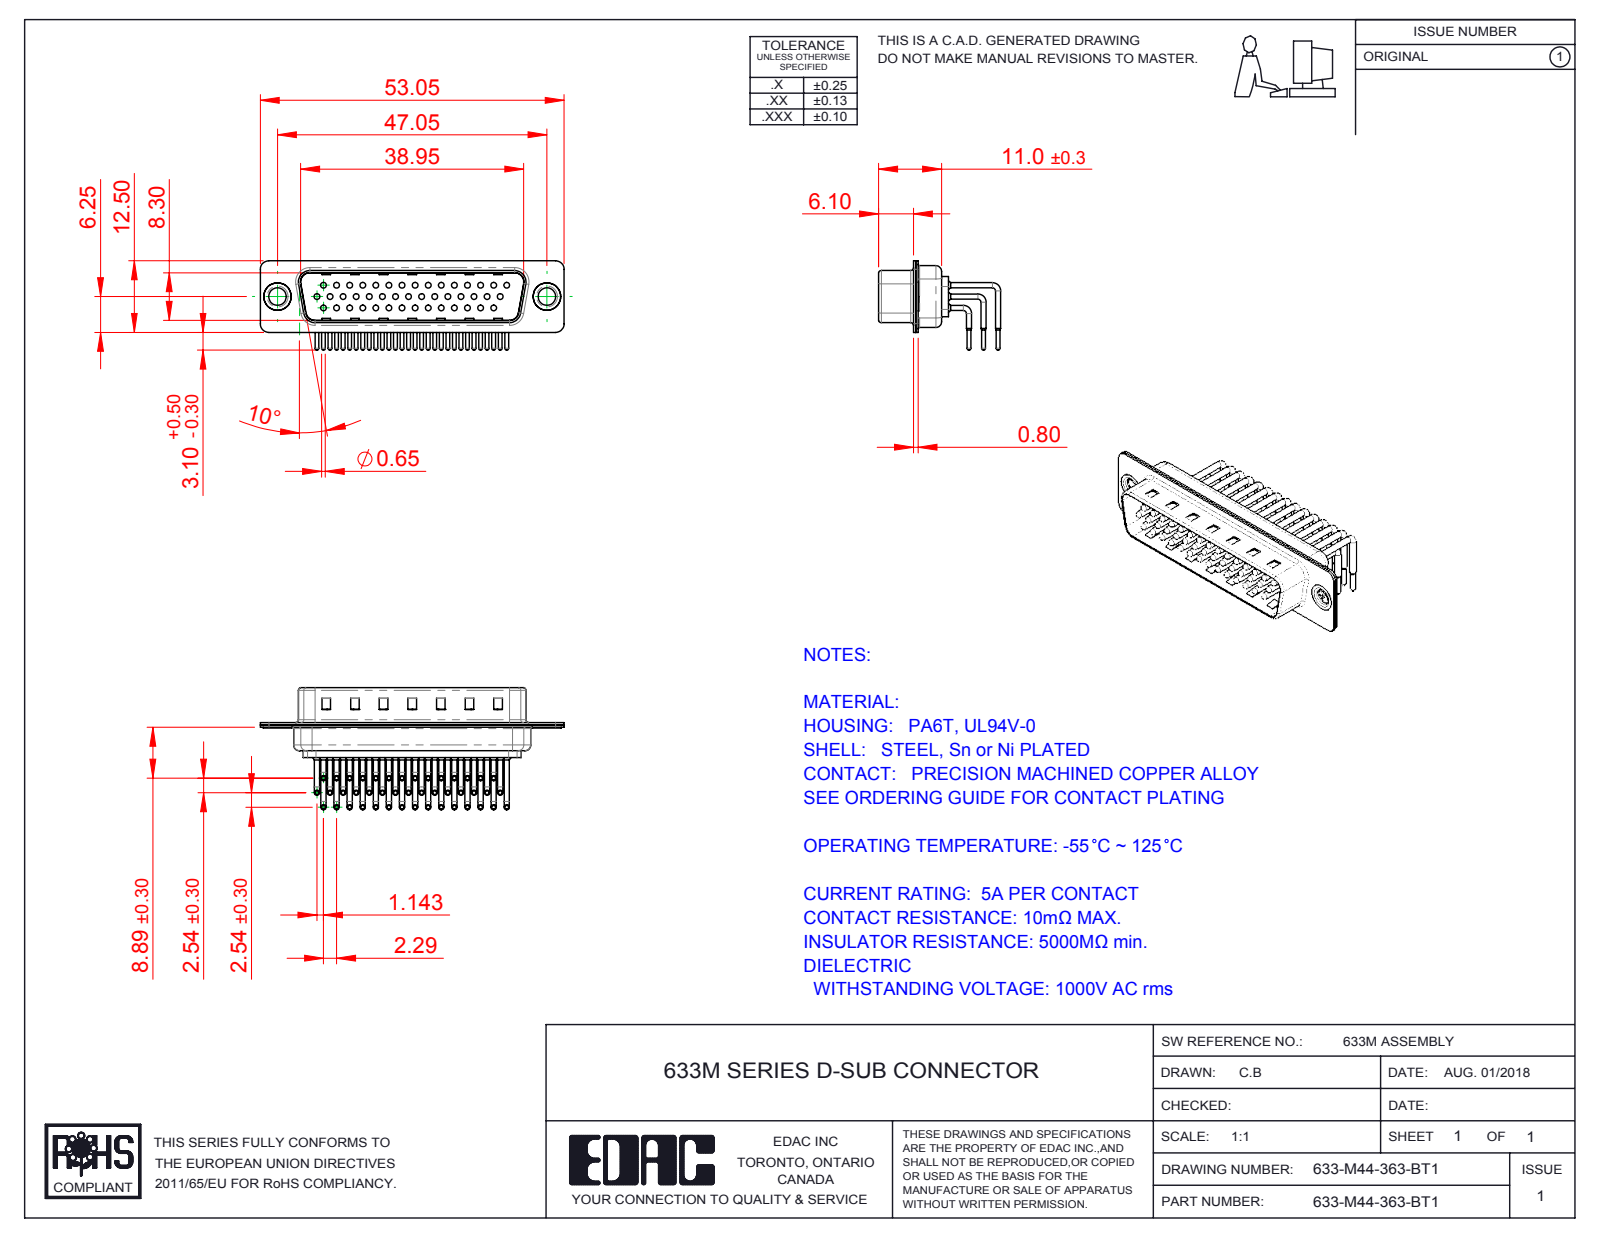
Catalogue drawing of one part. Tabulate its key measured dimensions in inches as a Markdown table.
| quantity | value |
| --- | --- |
| part name | 633-M44-363-BT1; 633M Shell Rear_44 Contacts; 633M Shell Front_44 Contacts; 633M Housing_44 Contacts (+4 more) |
| STEP written by | SolidWorks 2016 (CONFIG_CONTROL_DESIGN) |
| units | inches |
| bodies | 49 solids, 5190 faces (2987 planar, 1705 cylindrical, 498 other) |
| overall size | 2.089 × 0.839 × 0.614 |
| volume | 0.187 in³ |
| surface area | 15.35 in² |
| round holes (diameter × count) | 0.039 × 44, 0.067 × 44, 0.079 × 44, 0.12 × 2, 0.157 × 2, 0.189 × 2 |
| round bosses / shafts (diameter × count) | 0.035 × 88, 0.059 × 44, 0.026 × 44, 0.197 × 2, 0.193 × 2, 0.14 × 2, 0.039 × 2 |
| partial cylindrical surfaces (radius × count) | 0.04 × 44, 0.059 × 16, 0.079 × 12, 0.02 × 8, 0.063 × 8, 0.01 × 4, 0.024 × 4, 0.026 × 4 |
| main face-to-face distances | 0.016, 0.033, 0.376, 0.059, 0.343, 0.075, 0.049, 0.409, 0.014, 0.36 |
| hole center spacings | 0.09, 0.156, 0.09, 0.18, 0.324, 0.27, 0.45, 0.501 |
